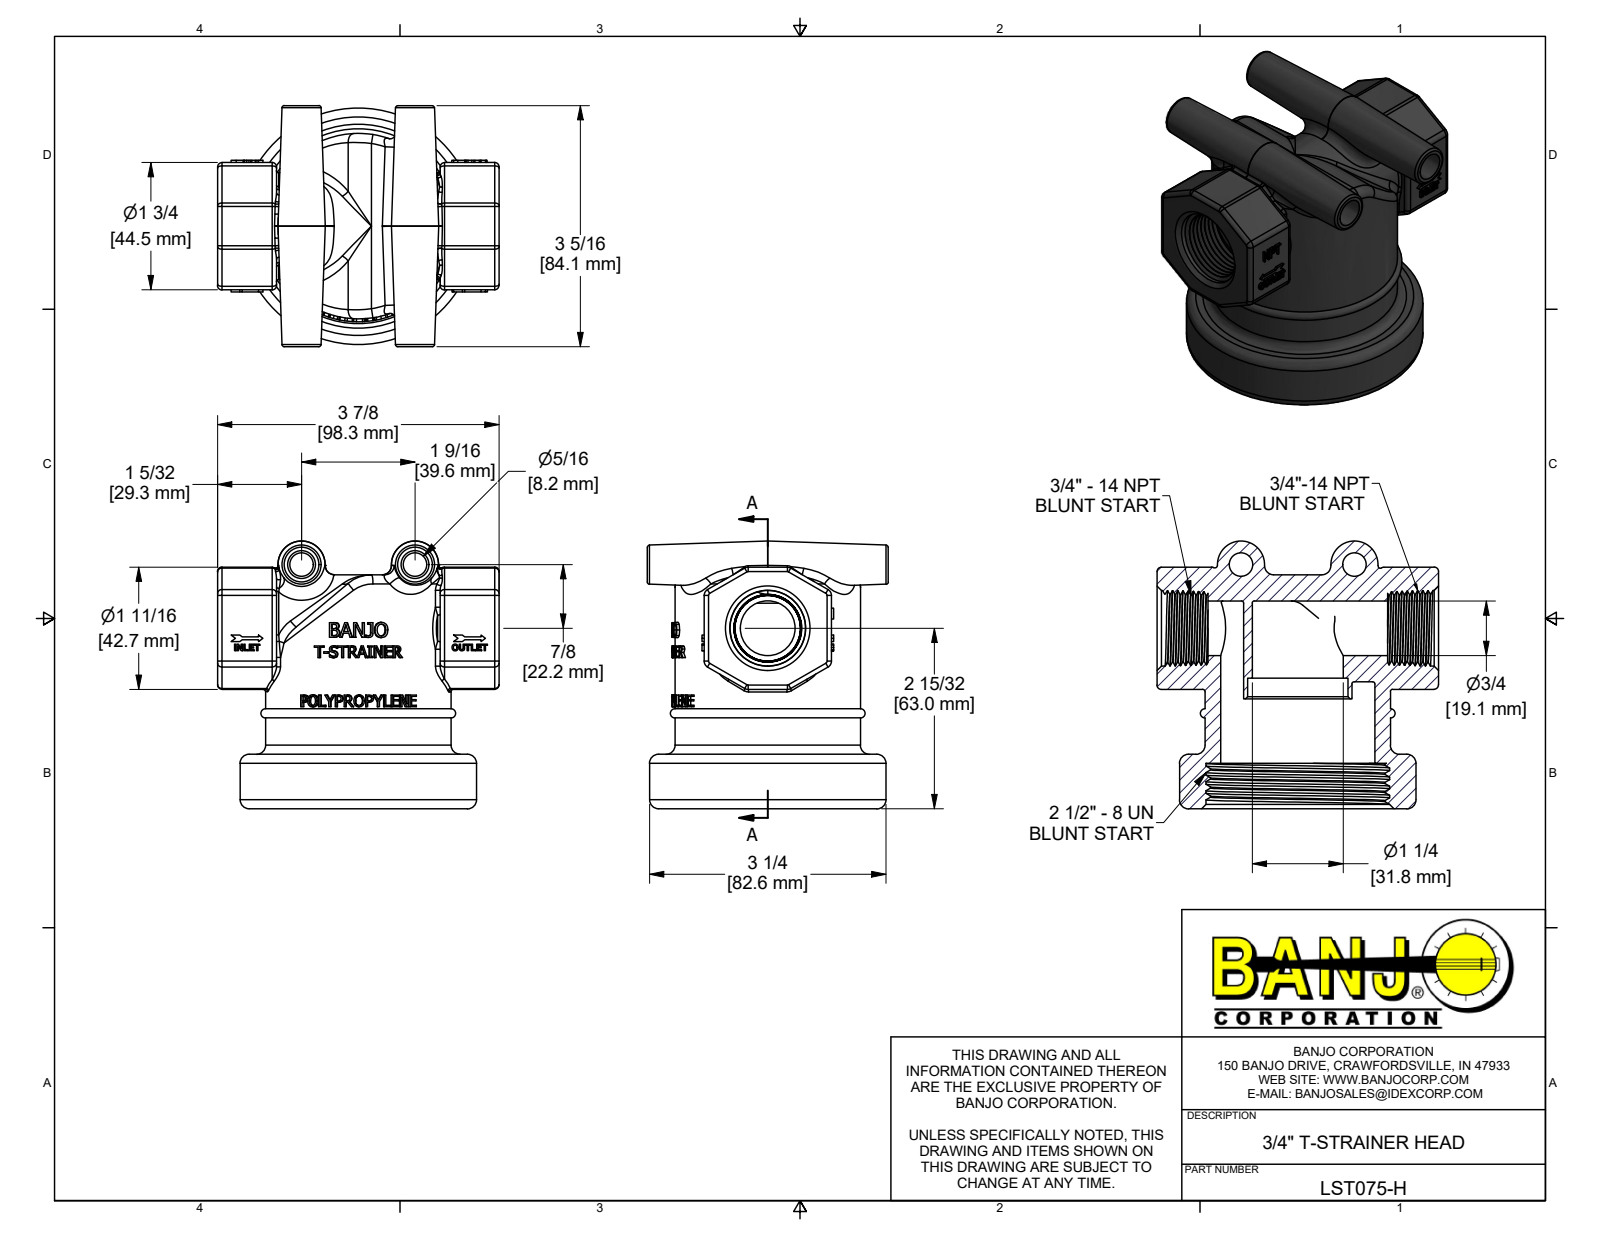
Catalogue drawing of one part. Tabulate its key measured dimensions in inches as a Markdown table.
| quantity | value |
| --- | --- |
| part name | LST075-H |
| STEP written by | Autodesk Inventor 2019 (AUTOMOTIVE_DESIGN) |
| units | inches |
| bodies | 1 solid, 1060 faces (533 planar, 123 cylindrical, 404 other) |
| overall size | 3.87 × 3.681 × 3.312 |
| volume | 12.08 in³ |
| surface area | 106.2 in² |
| round holes (diameter × count) | 0.75 × 1, 1.25 × 1, 1.38 × 1, 2.12 × 1, 2.396 × 1, 2.525 × 1 |
| round bosses / shafts (diameter × count) | 3.25 × 1, 2.55 × 1, 1.49 × 1, 1.47 × 1 |
| partial cylindrical surfaces (radius × count) | 0.06 × 30, 0.094 × 8, 0.03 × 2, 0.035 × 2, 0.25 × 1, 0.313 × 1, 0.5 × 1, 0.696 × 1 |
| main face-to-face distances | 1.75, 0.625, 3.87, 2.856, 2.231, 0.125, 0.75, 2.106, 3.321, 2.696 |
